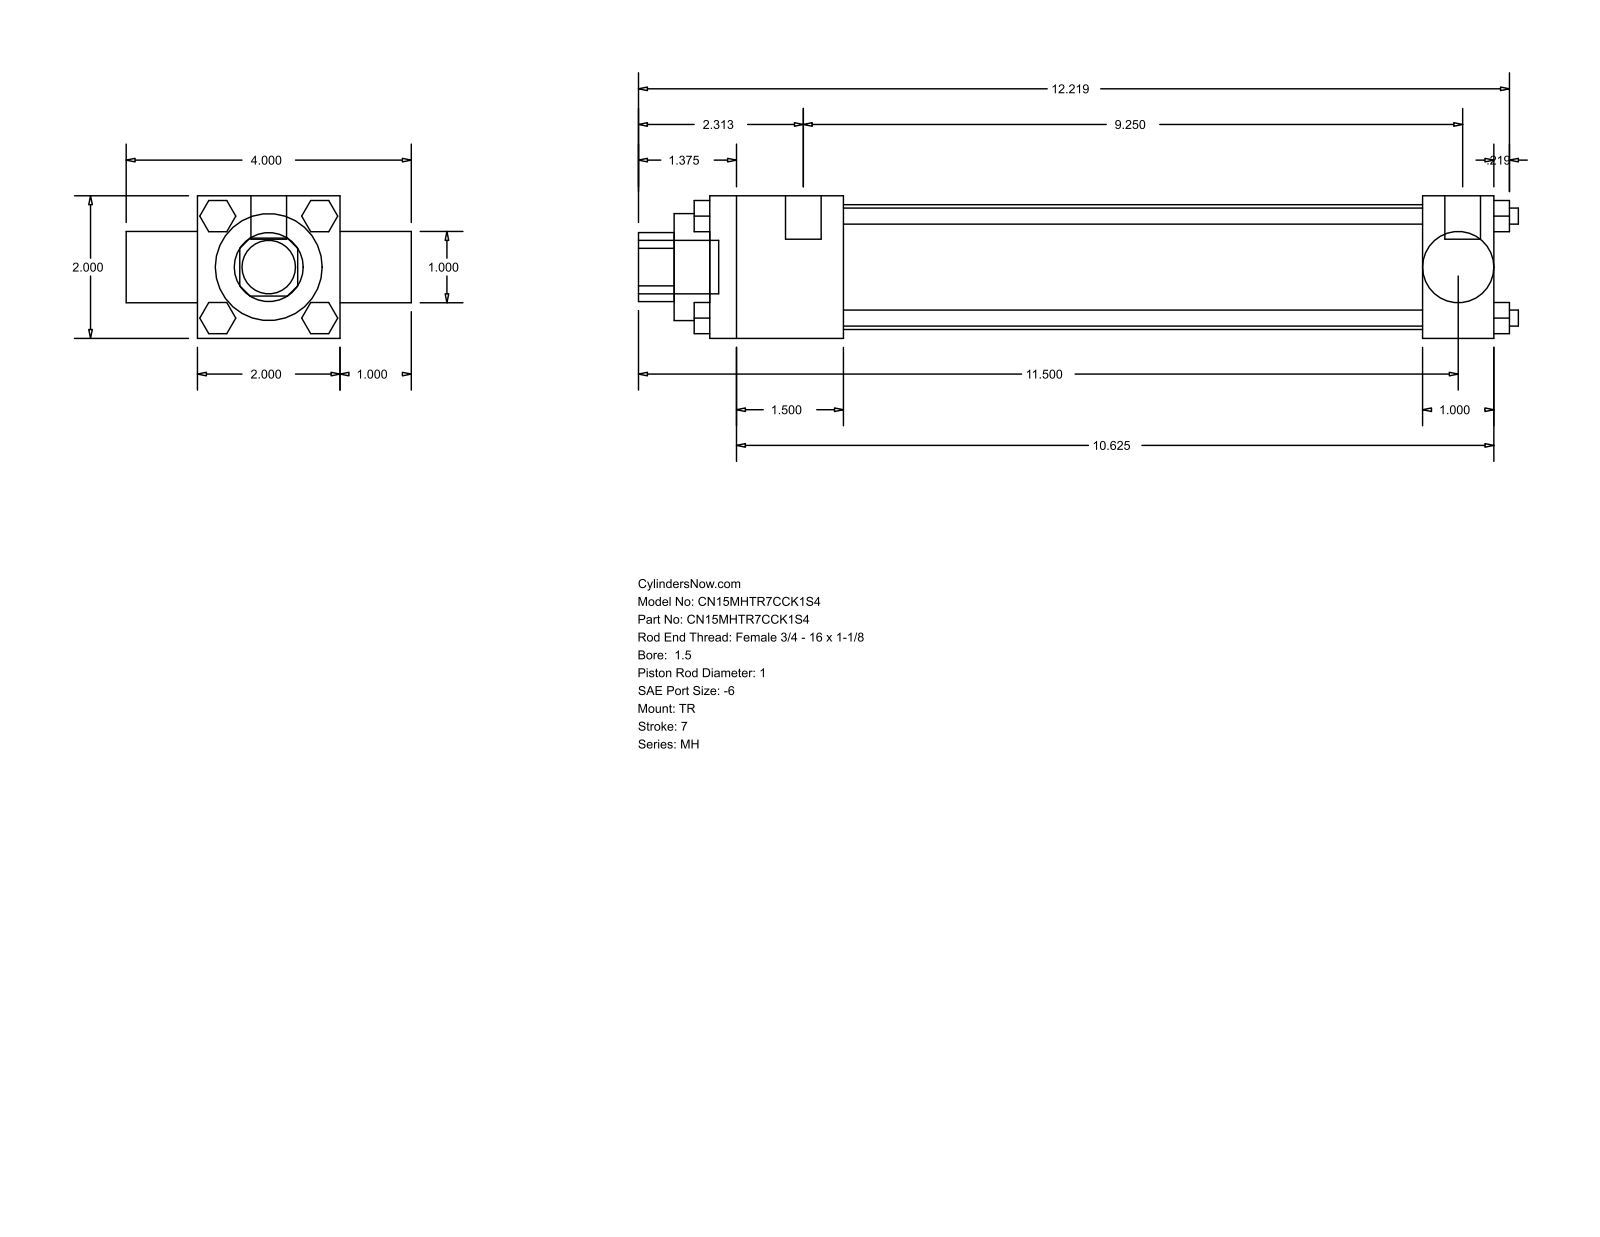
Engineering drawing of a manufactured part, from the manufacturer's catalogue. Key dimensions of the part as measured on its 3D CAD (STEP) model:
Part name (STEP PRODUCT): MH_TR__0150_1
STEP written by: GSSL Pune (CONFIG_CONTROL_DESIGN)
Units: millimetres
Bodies: 0 solids, 120 faces (92 planar, 28 cylindrical, 0 other)
Overall size (bounding box): 313.53 × 101.6 × 50.8
Round holes (diameter × count): ⌀25.35 ×1, ⌀25.4 ×1, ⌀38.1 ×1, ⌀44.45 ×1
Round bosses / shafts (diameter × count): ⌀5.71 ×4, ⌀5.56 ×3, ⌀12.7 ×2, ⌀19.05 ×1
Partial cylindrical surfaces — rounded edges, fillets, slot ends (radius × count): R12.29 ×1
Main face-to-face distances: 50.8, 25.4, 279.4, 76.2, 47.63, 231.77, 254, 206.37, 284.96, 12.7
